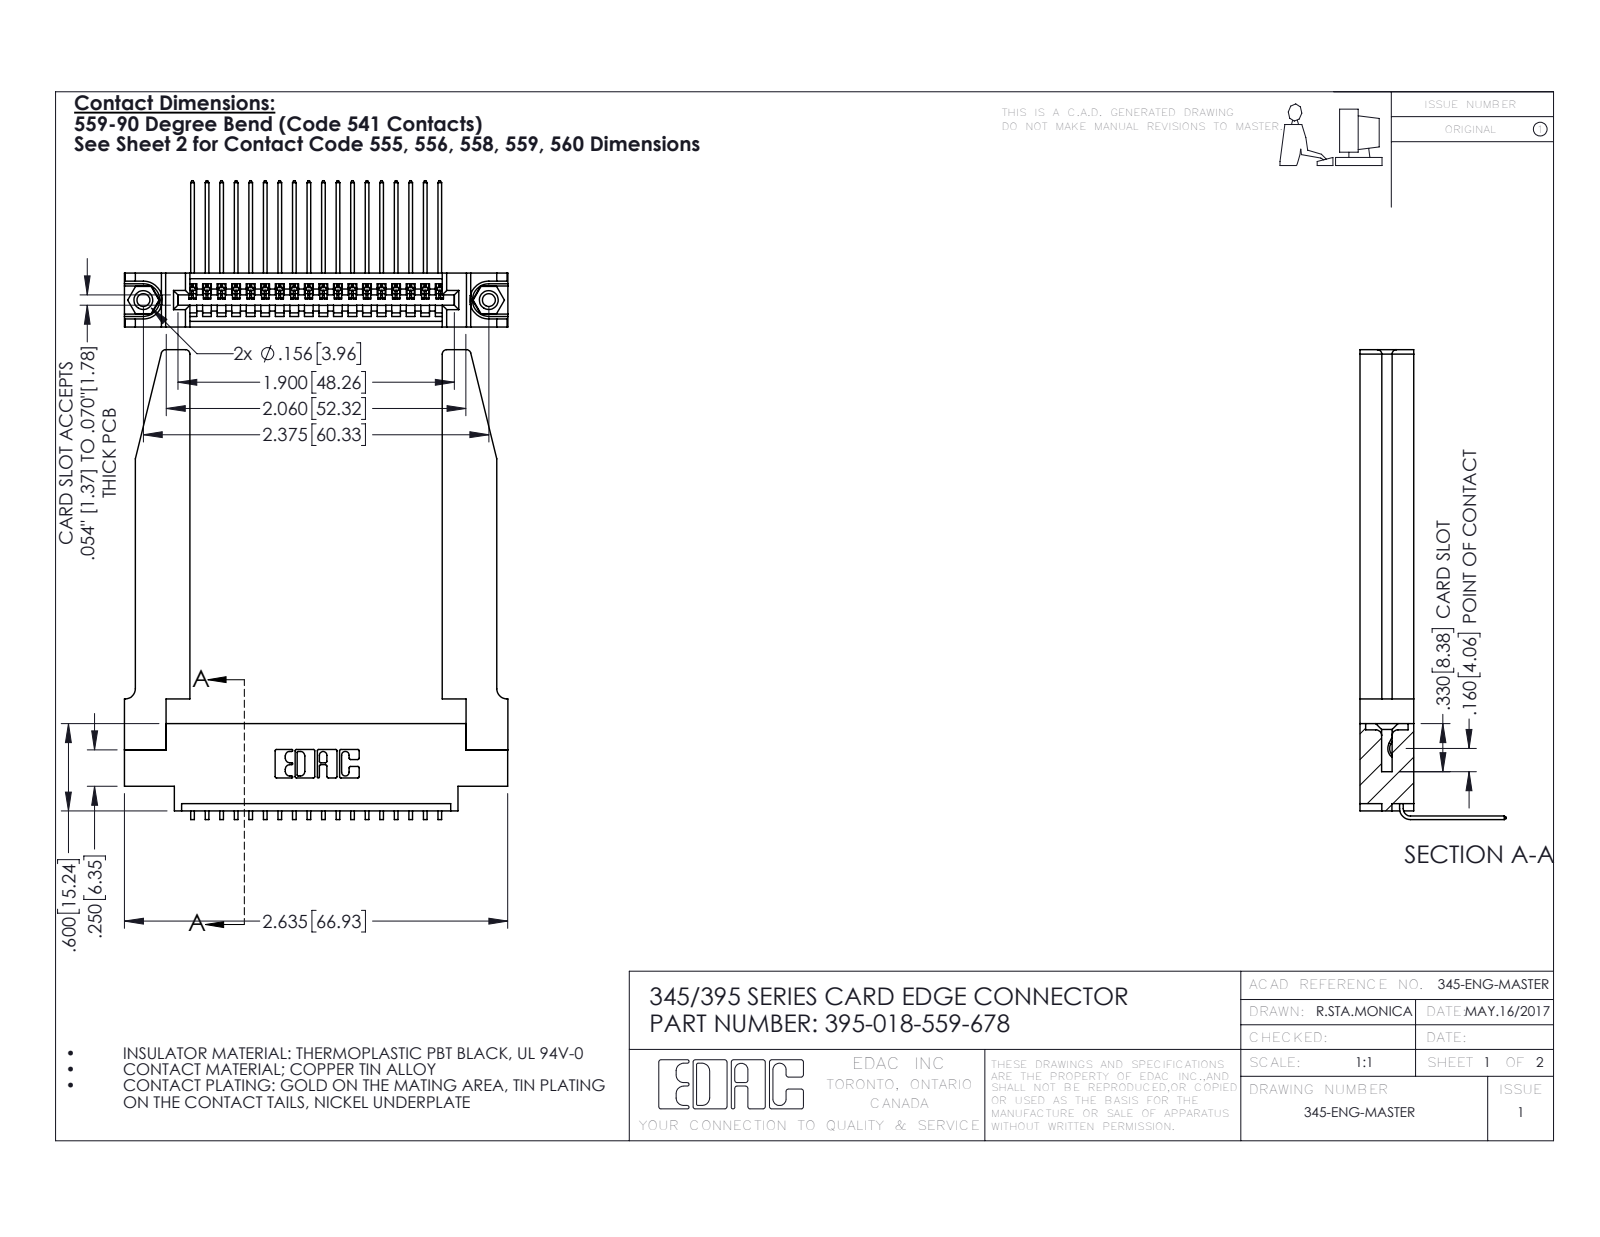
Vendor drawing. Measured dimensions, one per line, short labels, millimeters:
name: 345-250-001_345-250-001-102; 345-220-078_345-220-078; 345-292-001_558 559 Tail - 1; 395-018-559-678 (+1 more)
written by: SolidWorks 2016 (CONFIG_CONTROL_DESIGN)
unit: mm
bodies: 23 solids, 1444 faces (982 planar, 410 cylindrical, 52 other)
size: 82 × 67 × 25.5
volume: 13 900 mm³; area: 15 120 mm²
holes: 2× ⌀2.3, 2× ⌀3.2, 2× ⌀4, 1× ⌀1.6
bosses: 2× ⌀3.9
rounds: 36× R0.2, 22× R0.3, 8× R0.8, 6× R0.2, 6× R0.8, 3× R0.7, 2× R0.8, 2× R1
face distances: 9.4, 1.8, 7.6, 3.8, 3.8, 2.5, 6.9, 0.6, 5.1, 5.6
hole spacings: 6.9, 54.4, 60.3
